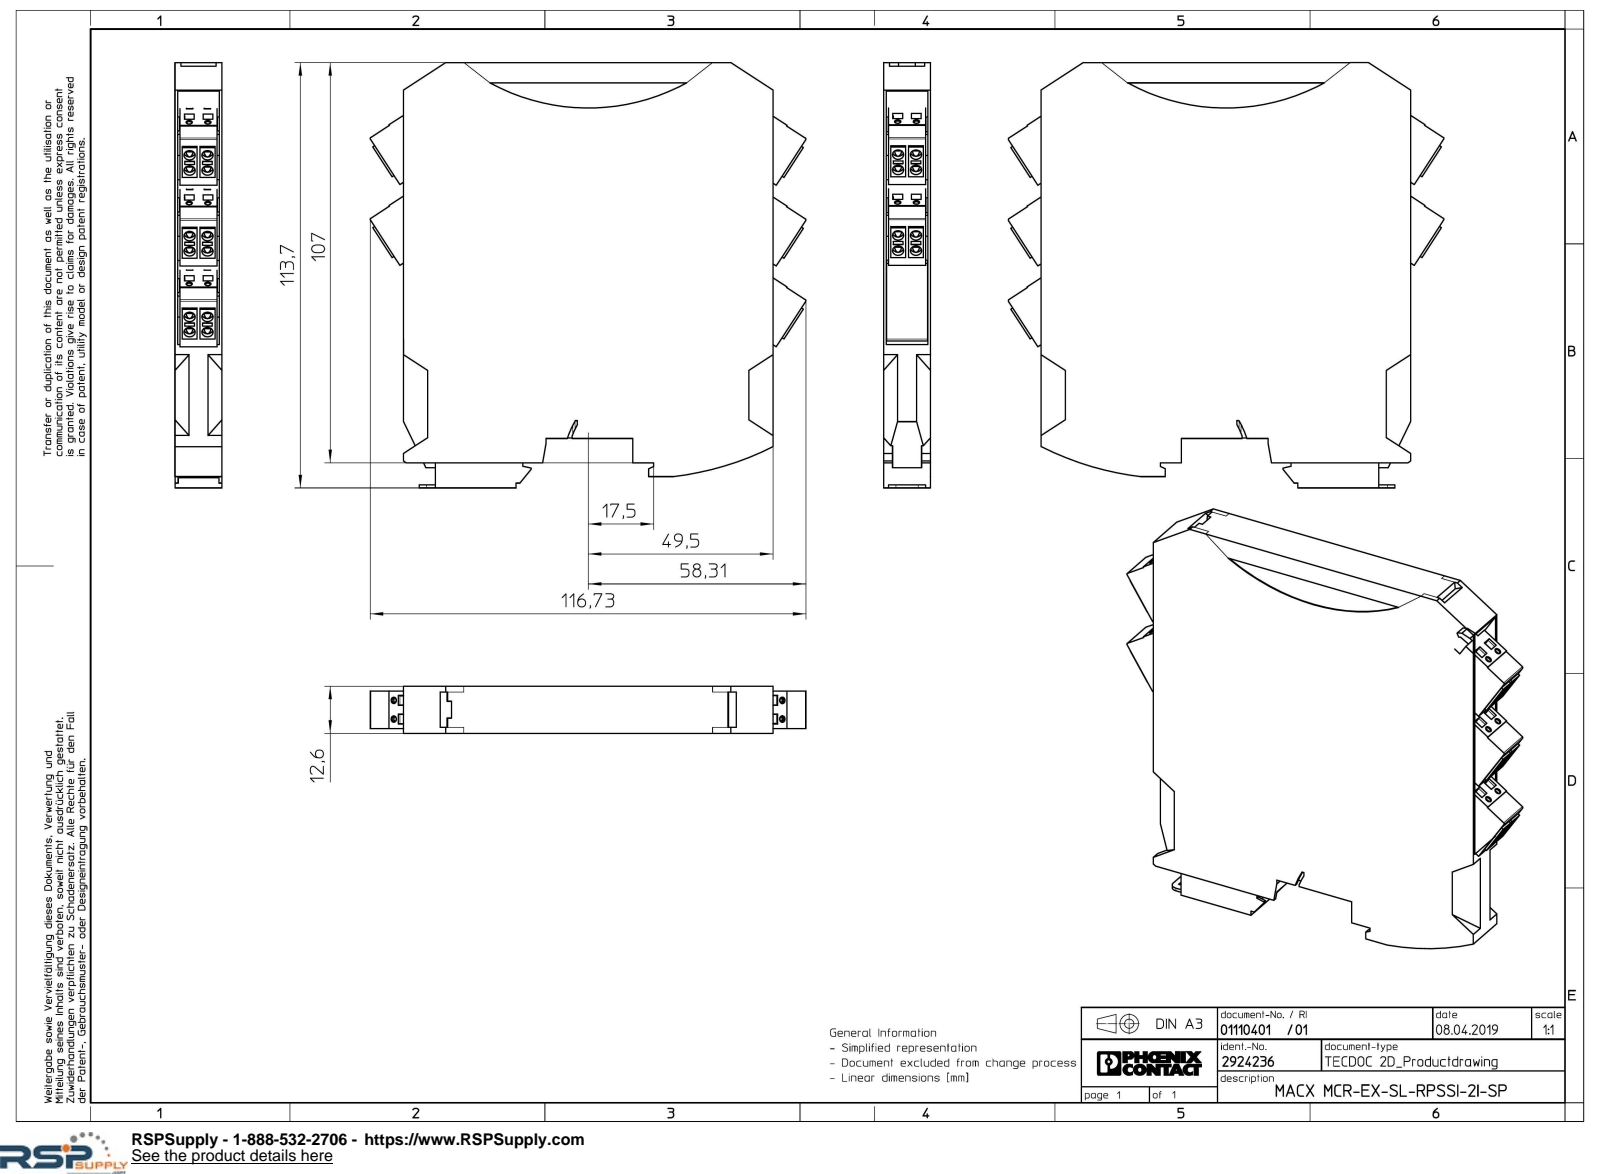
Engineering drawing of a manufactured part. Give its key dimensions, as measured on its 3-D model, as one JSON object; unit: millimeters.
{"part_name": "MAXC_12.5-GY-SOCKEL-select; ME_MAX_B-12.5_GY7042-select; TVFKC_1.5_2-ST_GY7035-select.3; TVFKC_1.5_2-ST_BU-select.1 (+1 more)", "step_written_by": "Creo Elements/Direct Modeling 20.1A 29-Sep-2018 (C) Parametric Technology GmbH (AUTOMOTIVE_DESIGN)", "units": "millimeters", "bodies": {"solids": 7, "faces": 1180, "planar": 880, "cylindrical": 210, "other": 90}, "overall_size": [116.67, 113.7, 12.6], "volume_mm3": 129676, "surface_area_mm2": 42737, "round_holes": [[3, 30], [1.3, 10], [1.53, 10]], "round_bosses_or_shafts": [[2.8, 6]], "partial_cylinders_radius": [[1.25, 20], [3, 13], [2, 10], [2.9, 10], [0.3, 7], [1.4, 6], [0.2, 2], [0.5, 1]], "face_to_face_distances": [12.6, 11.3, 1.3, 0.55, 0.75, 10.55, 11.85, 18.12, 10, 11.1], "hole_center_spacings": [18.11, 1.23, 4.8, 5, 5.05, 3.63, 6.1, 6.82]}
